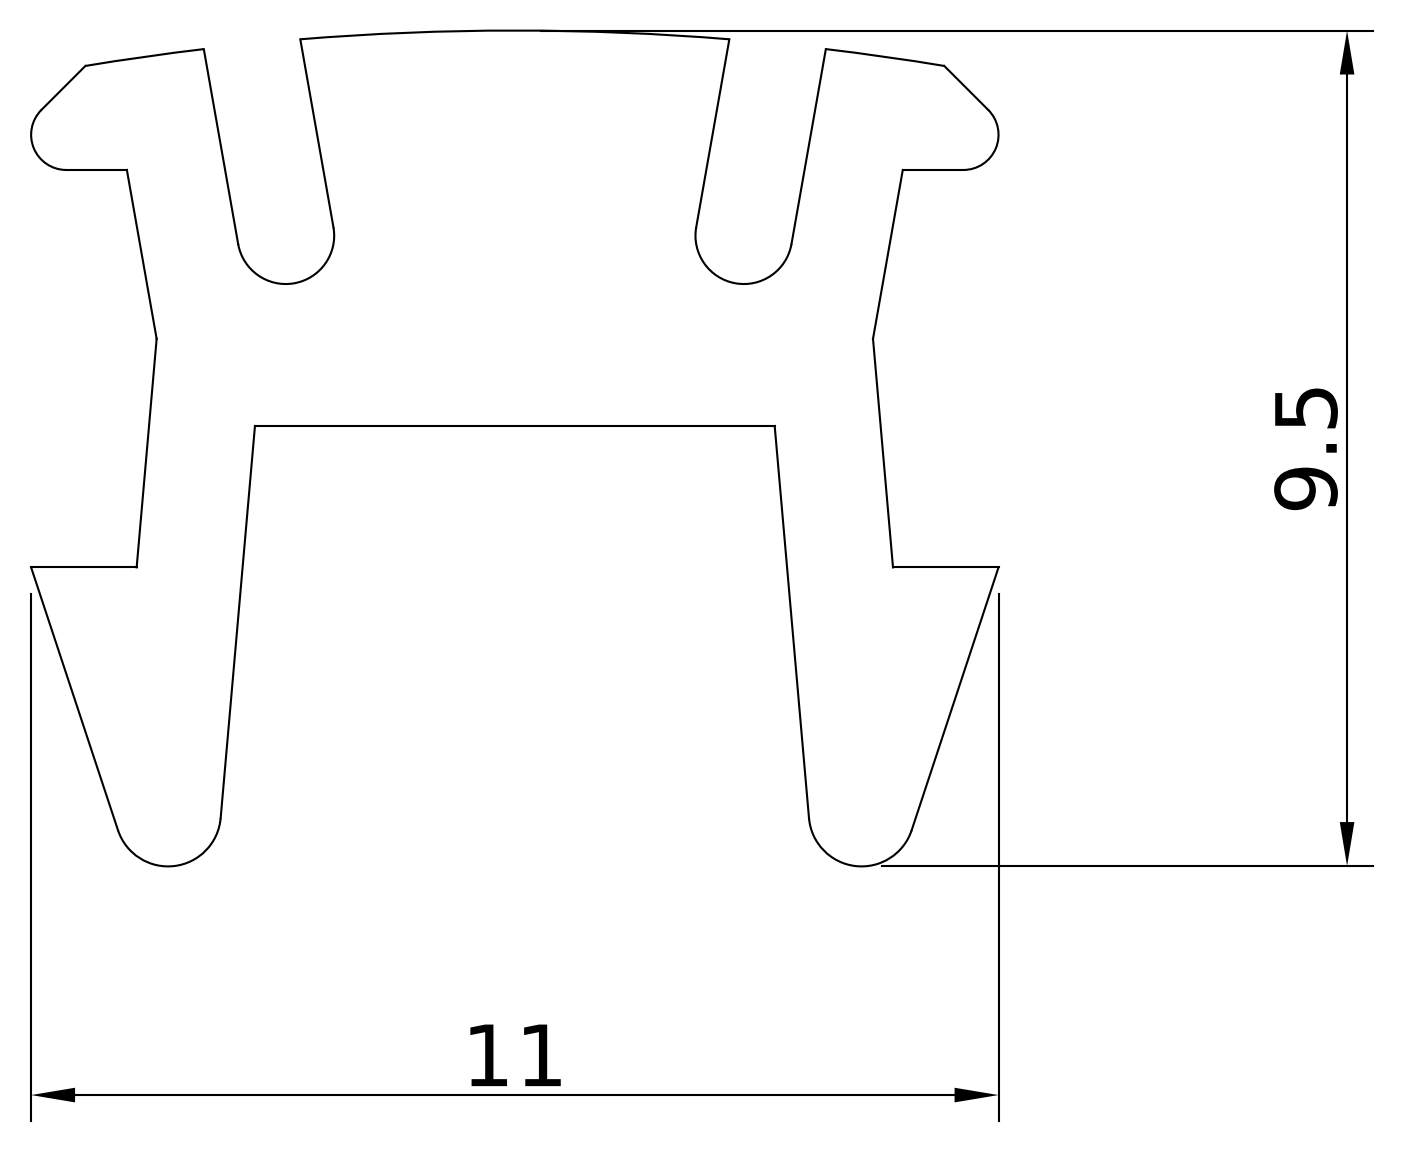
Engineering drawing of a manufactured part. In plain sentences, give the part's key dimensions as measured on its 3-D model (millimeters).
The part is named "DGUCA0000013". Its 3-D file was written by "Autodesk Inventor 2019 (AUTOMOTIVE_DESIGN)". It is 1 solid with 30 faces: 21 planar, 9 cylindrical and 0 other. Overall it measures 100 by 11 by 10.1 millimeters. Its volume is 4 999 cubic millimeters and its surface area 6 481 square millimeters. Partial cylindrical surfaces (rounded edges, fillets, slot ends): 2 of radius 0.4, 2 of radius 0.55, 2 of radius 0.6, 1 of radius 30. The main face-to-face distances are 1.1, 1.2, 2.2, 2.21, 1.11, 5.12, 2.92, 100.
